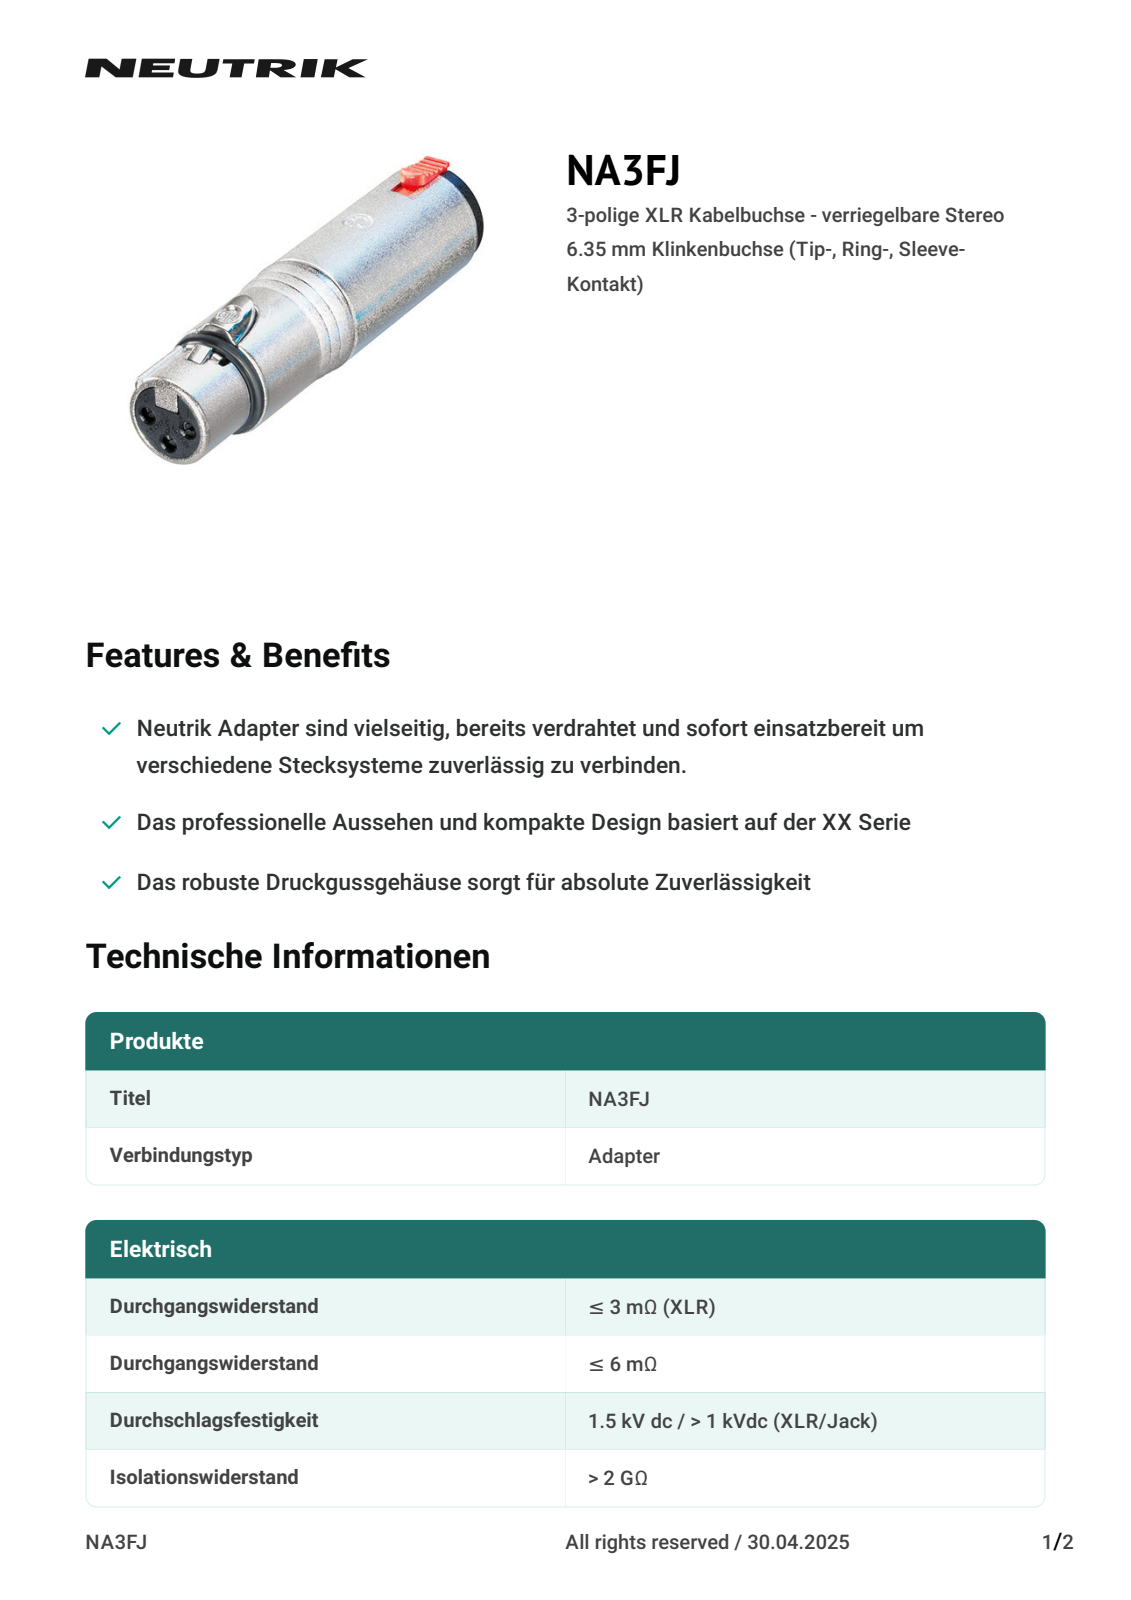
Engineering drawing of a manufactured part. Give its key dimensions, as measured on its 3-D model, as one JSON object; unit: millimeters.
{"part_name": "NA3FJ", "step_written_by": "CREO PARAMETRIC BY PTC INC, 2018360 (CONFIG_CONTROL_DESIGN)", "units": "millimeters", "bodies": {"solids": 1, "faces": 589, "planar": 230, "cylindrical": 114, "other": 245}, "overall_size": [80.5, 22, 20.97], "volume_mm3": 22836, "surface_area_mm2": 6024, "round_holes": [[5, 1], [5.1, 1], [6.5, 1], [13, 1]], "round_bosses_or_shafts": [[20, 1], [19.2, 1], [19, 1], [18.8, 1], [15.75, 1], [5, 1]], "partial_cylinders_radius": [[0.2, 23], [0.5, 10], [0.1, 6], [0.6, 4], [2.5, 3], [0.13, 2], [0.3, 2], [0.4, 2]], "face_to_face_distances": [79.3, 3.3, 76, 1, 77, 80.3, 4.3, 13.1, 0.6, 0.5]}
